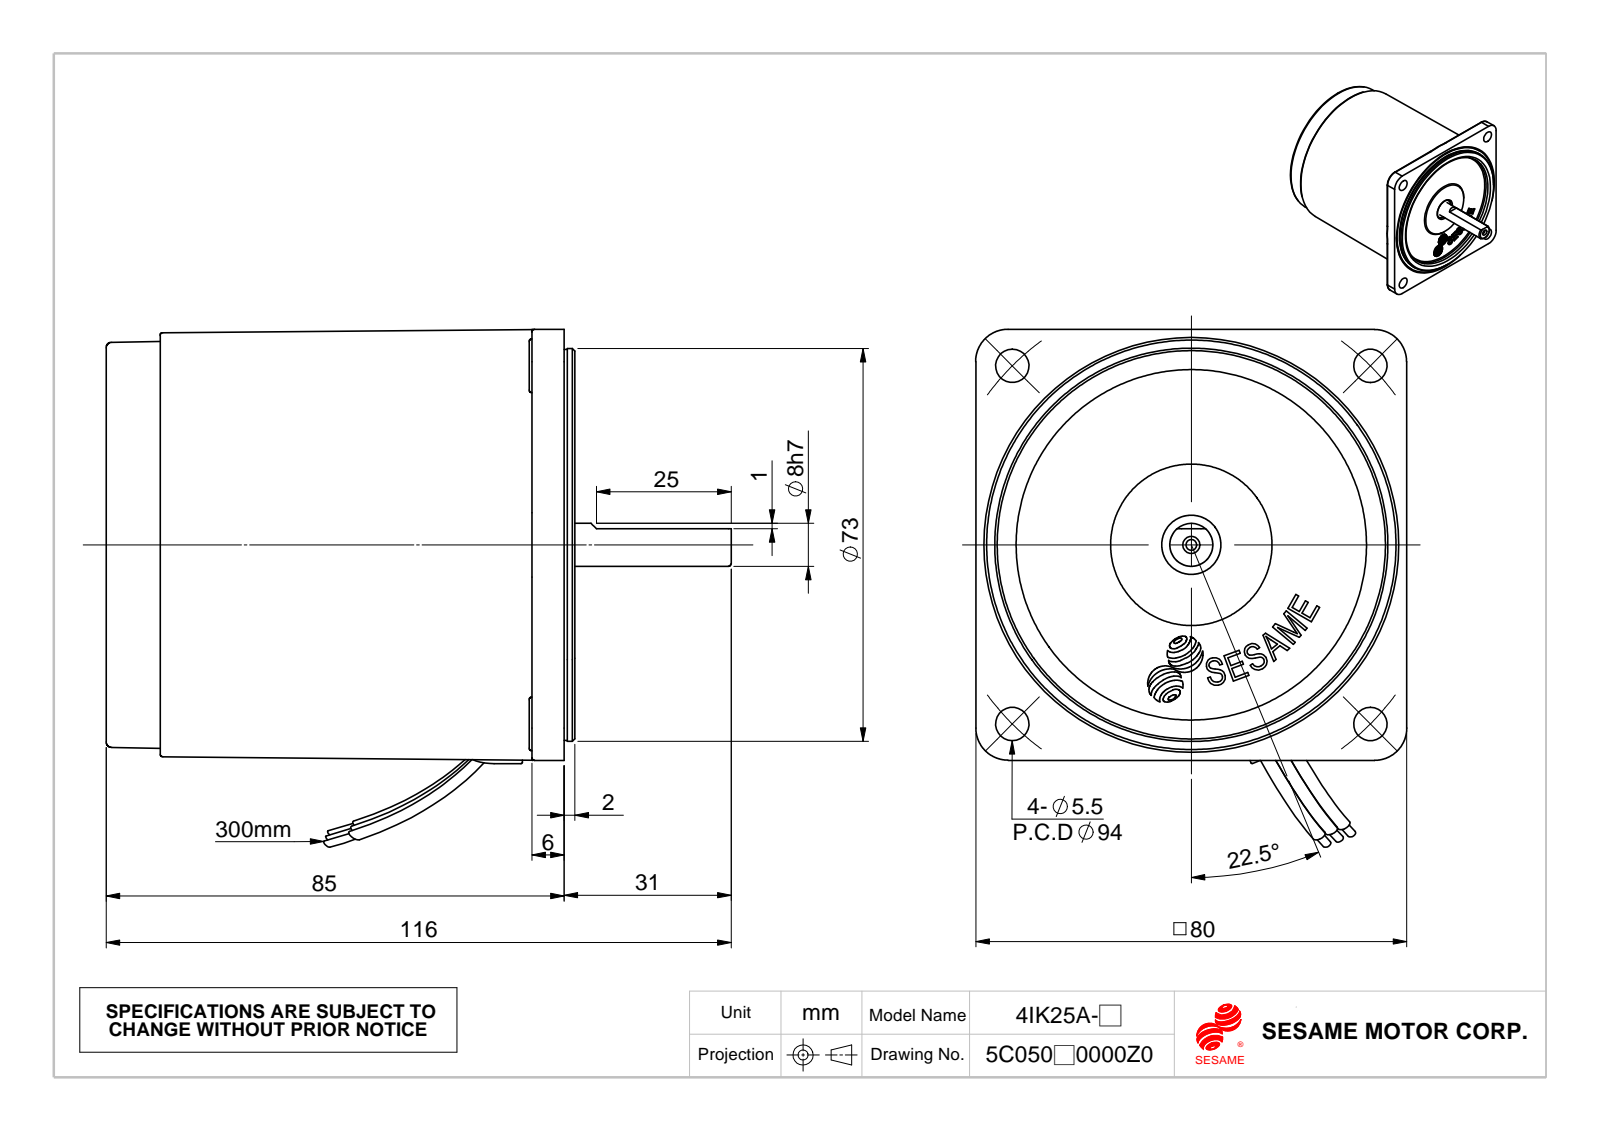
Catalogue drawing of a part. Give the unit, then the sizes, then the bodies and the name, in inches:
Units: inches
Overall size (bounding box): 4.567 × 3.784 × 3.15
Round holes (diameter × count): ⌀0.244 ×4, ⌀0.079 ×1, ⌀0.283 ×1, ⌀0.374 ×1, ⌀0.433 ×1, ⌀2.362 ×1, ⌀2.559 ×1, ⌀2.969 ×1
Round bosses / shafts (diameter × count): ⌀2.992 ×1, ⌀2.955 ×1, ⌀2.871 ×1, ⌀2.856 ×1, ⌀0.366 ×1, ⌀0.315 ×1
Partial cylindrical surfaces — rounded edges, fillets, slot ends (radius × count): R0.01 ×8, R0.024 ×8, R0.046 ×8, R0.051 ×8, R0.089 ×8, R0.006 ×4, R0.018 ×4, R0.02 ×4
Main face-to-face distances: 0.039, 0.02, 3.307, 3.244, 3.248, 3.268, 0.024, 0.059, 0.063, 3.287
Hole centre spacings: 1.85, 2.617, 3.7
Volume: 25.63 in³ · Surface area: 76.98 in²
Bodies: 7 solids, 448 faces (135 planar, 192 cylindrical, 121 other)
Part name (STEP PRODUCT): M425A_成品; C475-C473_C475成品-車工; 25A_3.研磨; 線扣
STEP written by: SolidWorks 2010 (CONFIG_CONTROL_DESIGN)
